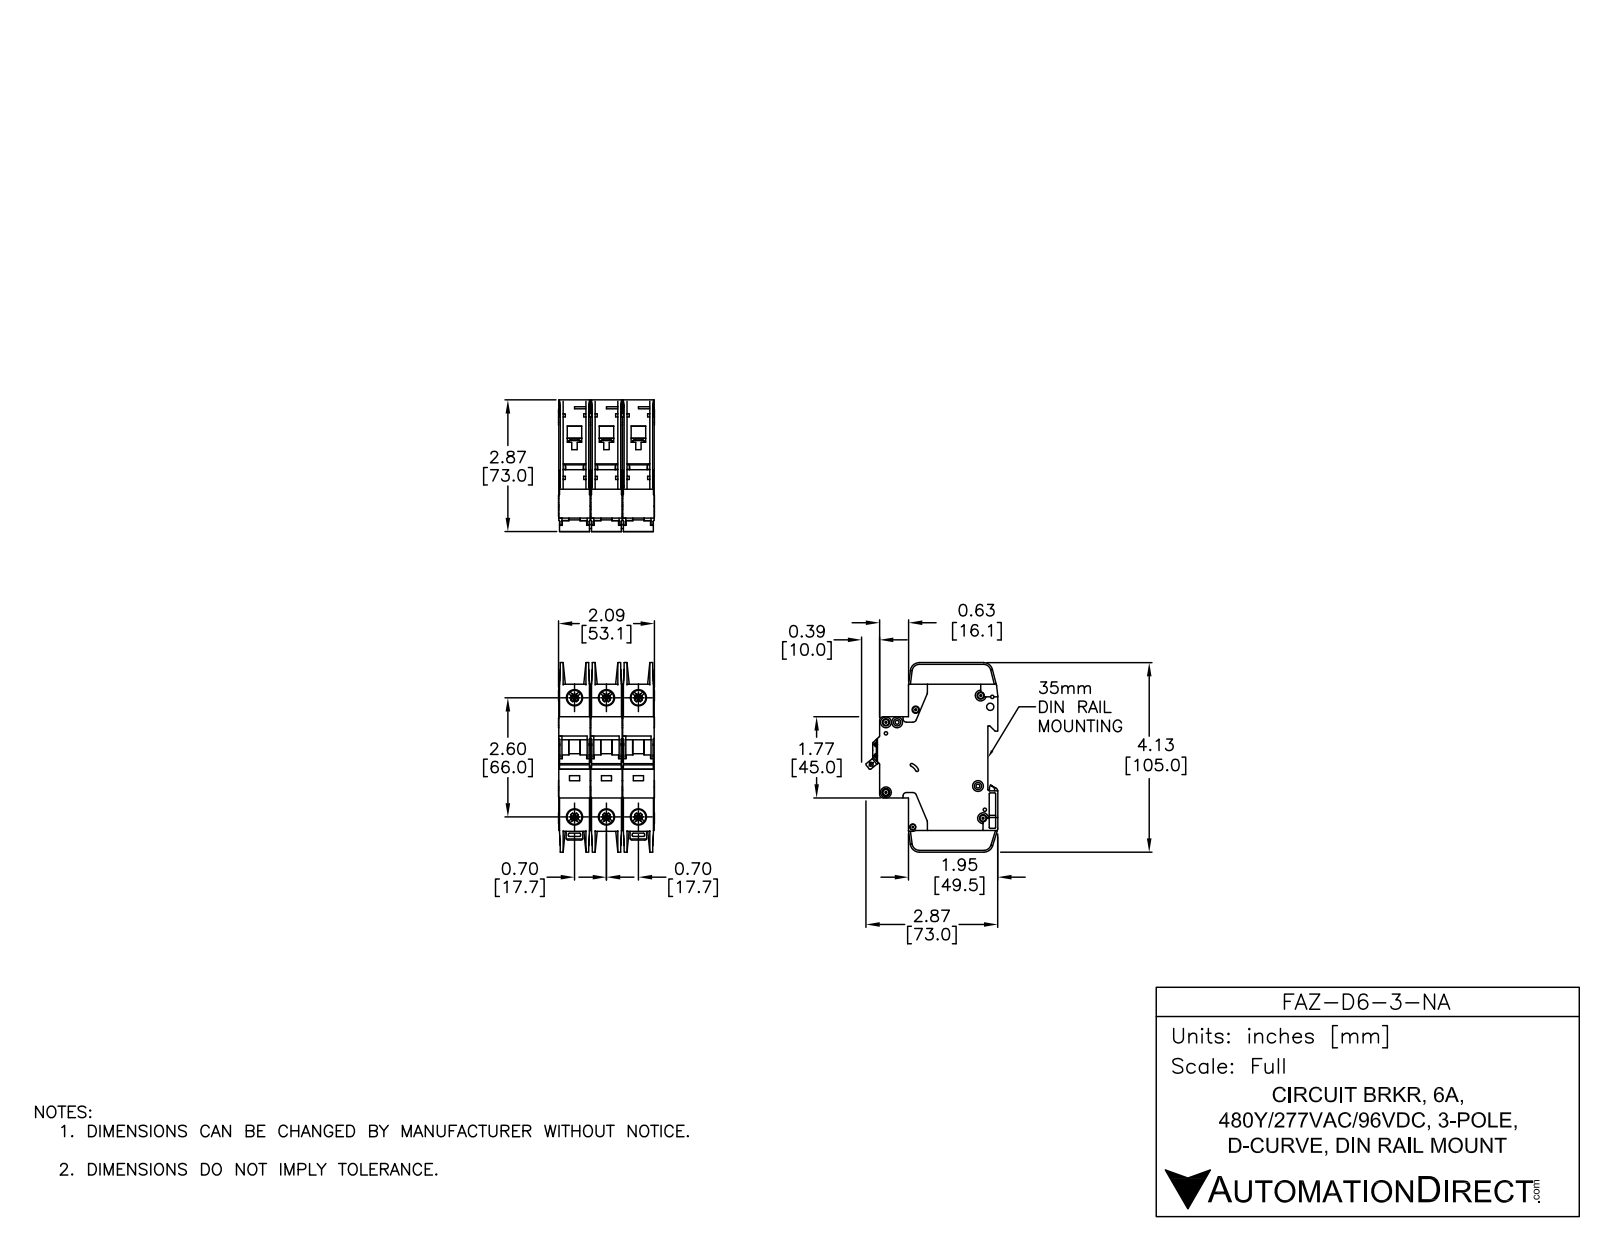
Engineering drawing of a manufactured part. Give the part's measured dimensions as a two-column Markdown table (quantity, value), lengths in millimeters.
| quantity | value |
| --- | --- |
| part name | FAZ-D6-3-NA |
| STEP written by | SolidWorks 2014 (AUTOMOTIVE_DESIGN) |
| units | millimeters |
| bodies | 9 solids, 2352 faces (1227 planar, 789 cylindrical, 336 other) |
| overall size | 105 × 73.04 × 53.1 |
| volume | 233 085 mm³ |
| surface area | 74 219 mm² |
| round holes (diameter × count) | 3.6 × 7, 7.15 × 6, 8.2 × 6, 1.09 × 2, 1.5 × 2, 4 × 2, 1.9 × 1, 2.15 × 1, 2.2 × 1, 2.55 × 1, 3.3 × 1, 3.4 × 1 |
| round bosses / shafts (diameter × count) | 6 × 7, 2.5 × 3 |
| partial cylindrical surfaces (radius × count) | 0.25 × 65, 0.5 × 30, 1 × 26, 2 × 14, 1.8 × 5, 5 × 5, 4 × 4, 0.2 × 2 |
| main face-to-face distances | 17.7, 35.4, 17.5, 35.2, 0.7, 15.05, 2.45, 1.75, 15.75, 13.3 |
| hole center spacings | 17.7, 68.33, 66, 6.2, 35.4, 74.89, 5.19, 6.1 |
